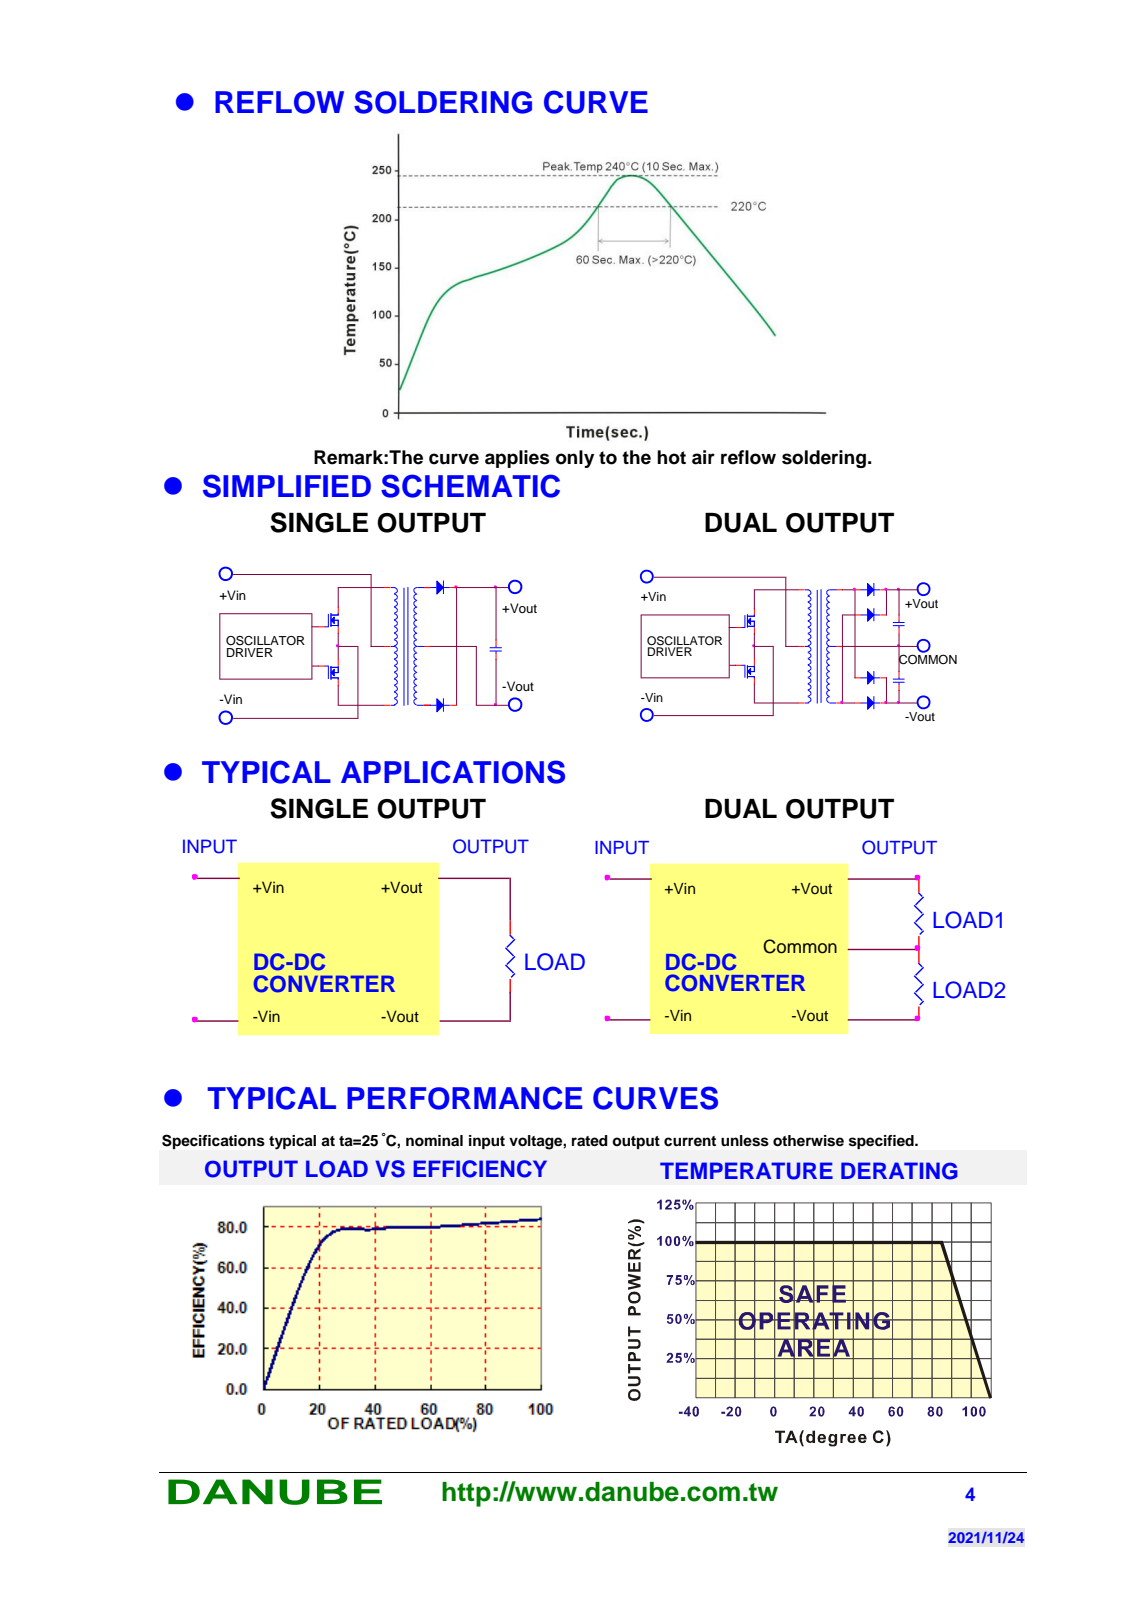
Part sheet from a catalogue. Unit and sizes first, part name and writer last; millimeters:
Units: millimetres
Overall size (bounding box): 15.24 × 11.1 × 7.05
Partial cylindrical surfaces — rounded edges, fillets, slot ends (radius × count): R1.2 ×4
Main face-to-face distances: 6.8, 0.5, 8.69, 15.24, 2.54, 6.3, 5.08, 10.16, 7.62, 8.44
Volume: 1 028 mm³ · Surface area: 701 mm²
Bodies: 11 solids, 139 faces (135 planar, 4 cylindrical, 0 other)
Part name (STEP PRODUCT): case; pin1; pin12; pin11 (+7 more)
STEP written by: FreeCAD (AUTOMOTIVE_DESIGN)
